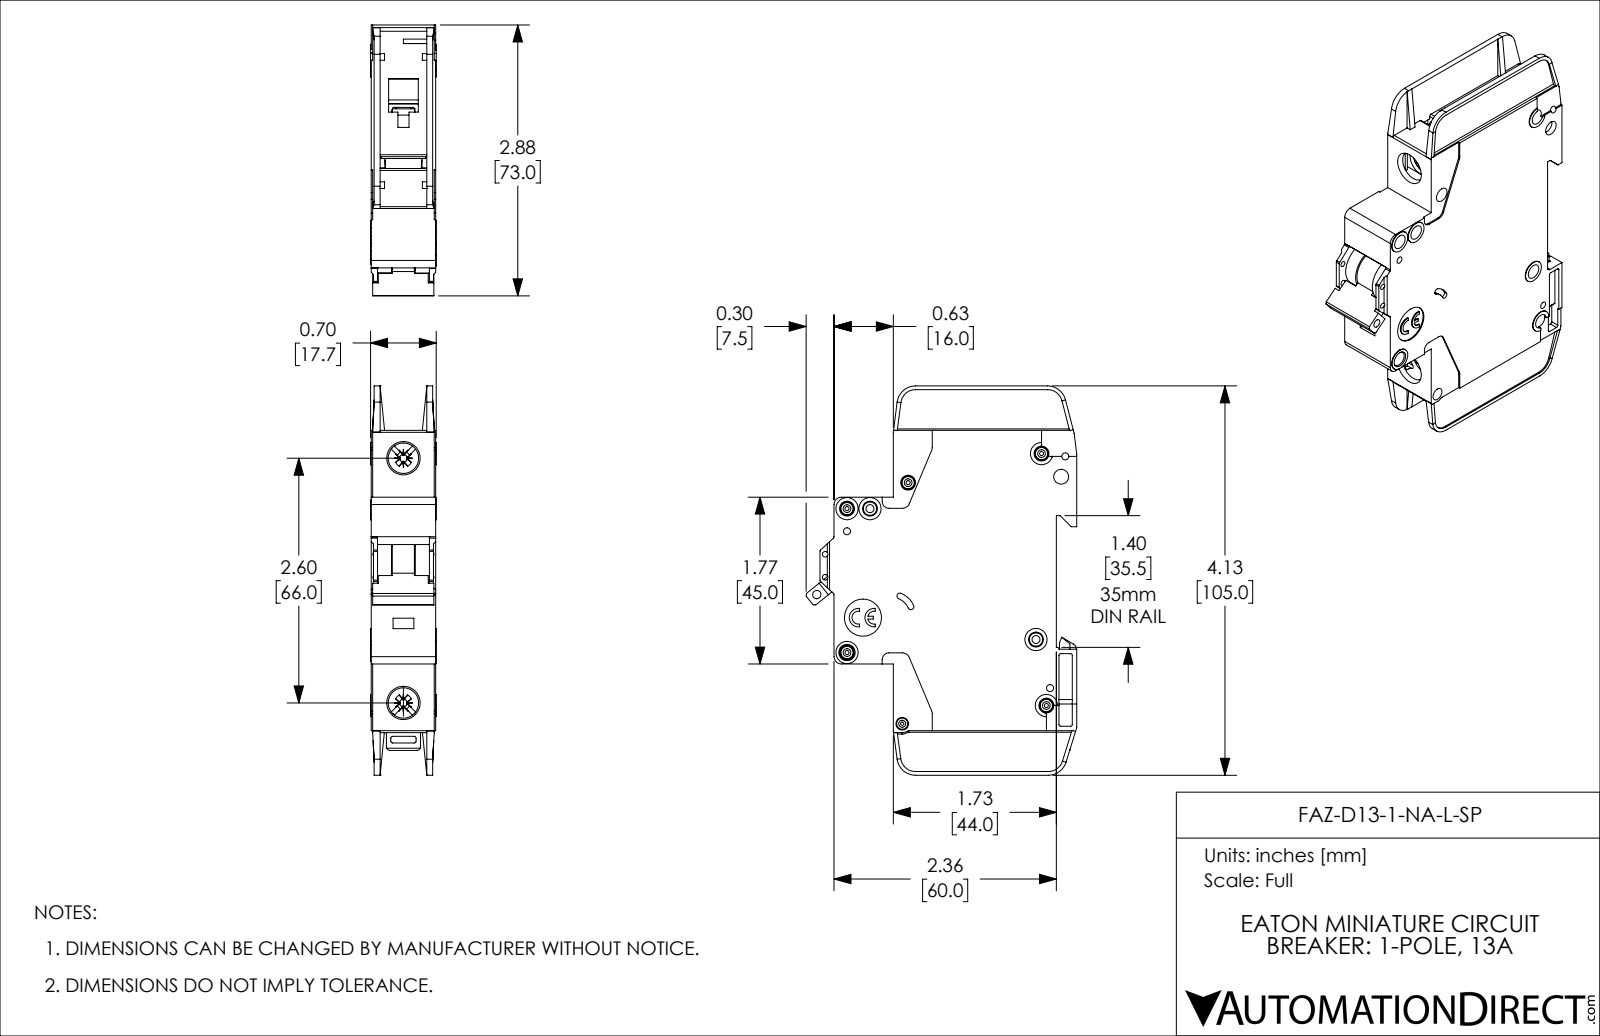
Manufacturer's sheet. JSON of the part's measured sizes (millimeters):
{"part_name": "FAZ-D13-1-NA-L-SP", "step_written_by": "SolidWorks 2019 (AUTOMOTIVE_DESIGN)", "units": "millimeters", "bodies": {"solids": 1, "faces": 1127, "planar": 671, "cylindrical": 357, "other": 99}, "overall_size": [105, 73.1, 17.7], "volume_mm3": 76720, "surface_area_mm2": 26460, "round_holes": [[4, 8], [1.1, 5], [1.9, 4], [1.5, 2], [2.2, 2], [8.2, 2], [0.9, 1], [2.3, 1], [2.5, 1], [3.4, 1], [10, 1]], "round_bosses_or_shafts": [[3.3, 5], [6, 4], [3, 2], [2.5, 1]], "partial_cylinders_radius": [[0.5, 42], [0.4, 10], [1, 10], [2, 8], [5, 5], [0.2, 4], [0.7, 4], [1.1, 4]], "face_to_face_distances": [1.2, 17.4, 15, 16.2, 2.4, 13.8, 0.4, 0.8, 12.6, 14.6], "hole_center_spacings": [6.2, 13.6, 22.1, 4.8, 5.1, 5.2, 5.6, 6.1]}
